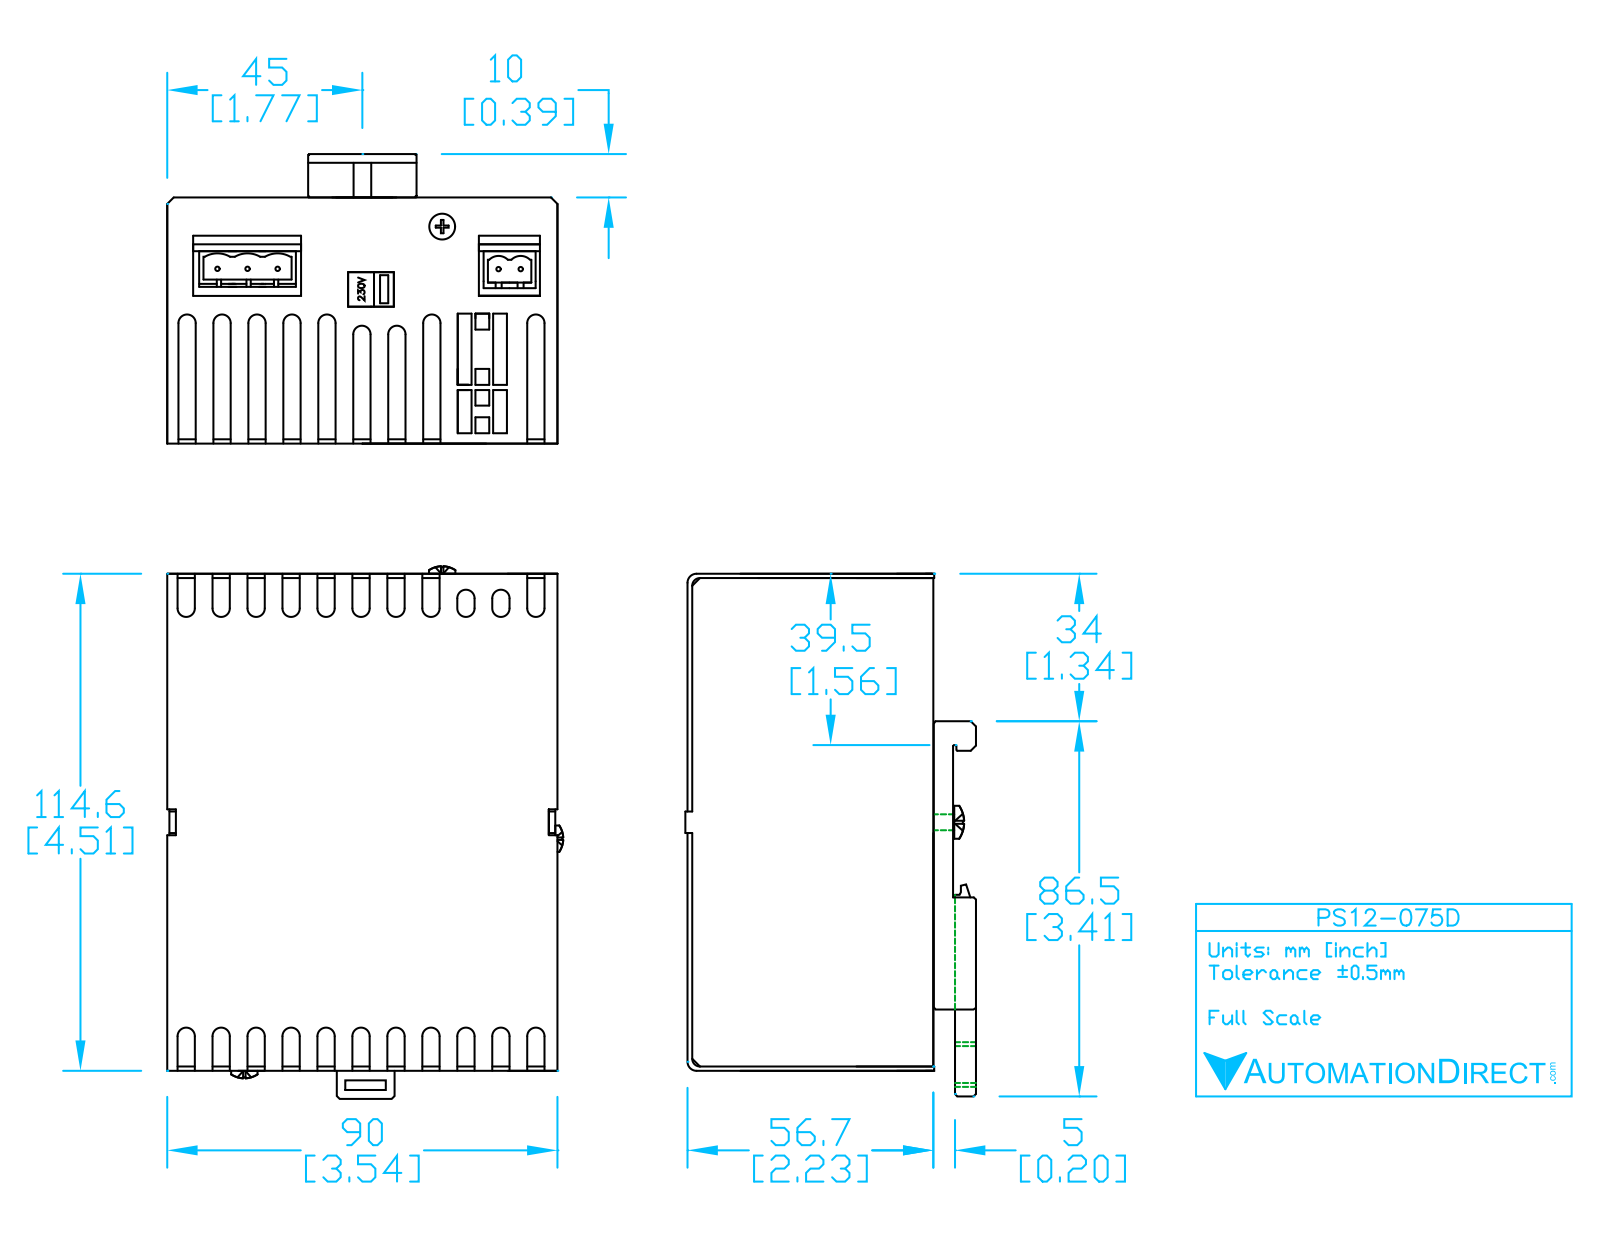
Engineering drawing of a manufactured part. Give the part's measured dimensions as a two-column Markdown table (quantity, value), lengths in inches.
| quantity | value |
| --- | --- |
| part name | PS12-075D |
| STEP written by | SolidWorks 2011 (CONFIG_CONTROL_DESIGN) |
| units | inches |
| bodies | 1 solid, 701 faces (458 planar, 169 cylindrical, 74 other) |
| overall size | 5.135 × 3.626 × 2.694 |
| volume | 22.13 in³ |
| surface area | 119.6 in² |
| round holes (diameter × count) | 0.15 × 5, 0.135 × 1 |
| round bosses / shafts (diameter × count) | 0.21 × 2, 0.3 × 1, 0.265 × 1, 0.212 × 1 |
| partial cylindrical surfaces (radius × count) | 0.076 × 59, 0.06 × 4, 0.015 × 2, 0.02 × 2, 0.05 × 2, 0.1 × 2 |
| main face-to-face distances | 0.04, 3.538, 4.47, 3.46, 0.039, 3.499, 2.495, 2.23, 2.229, 2.189 |
| hole center spacings | 0.2, 0.31, 0.315, 0.625, 1.444, 1.446, 2.073, 2.273 |
